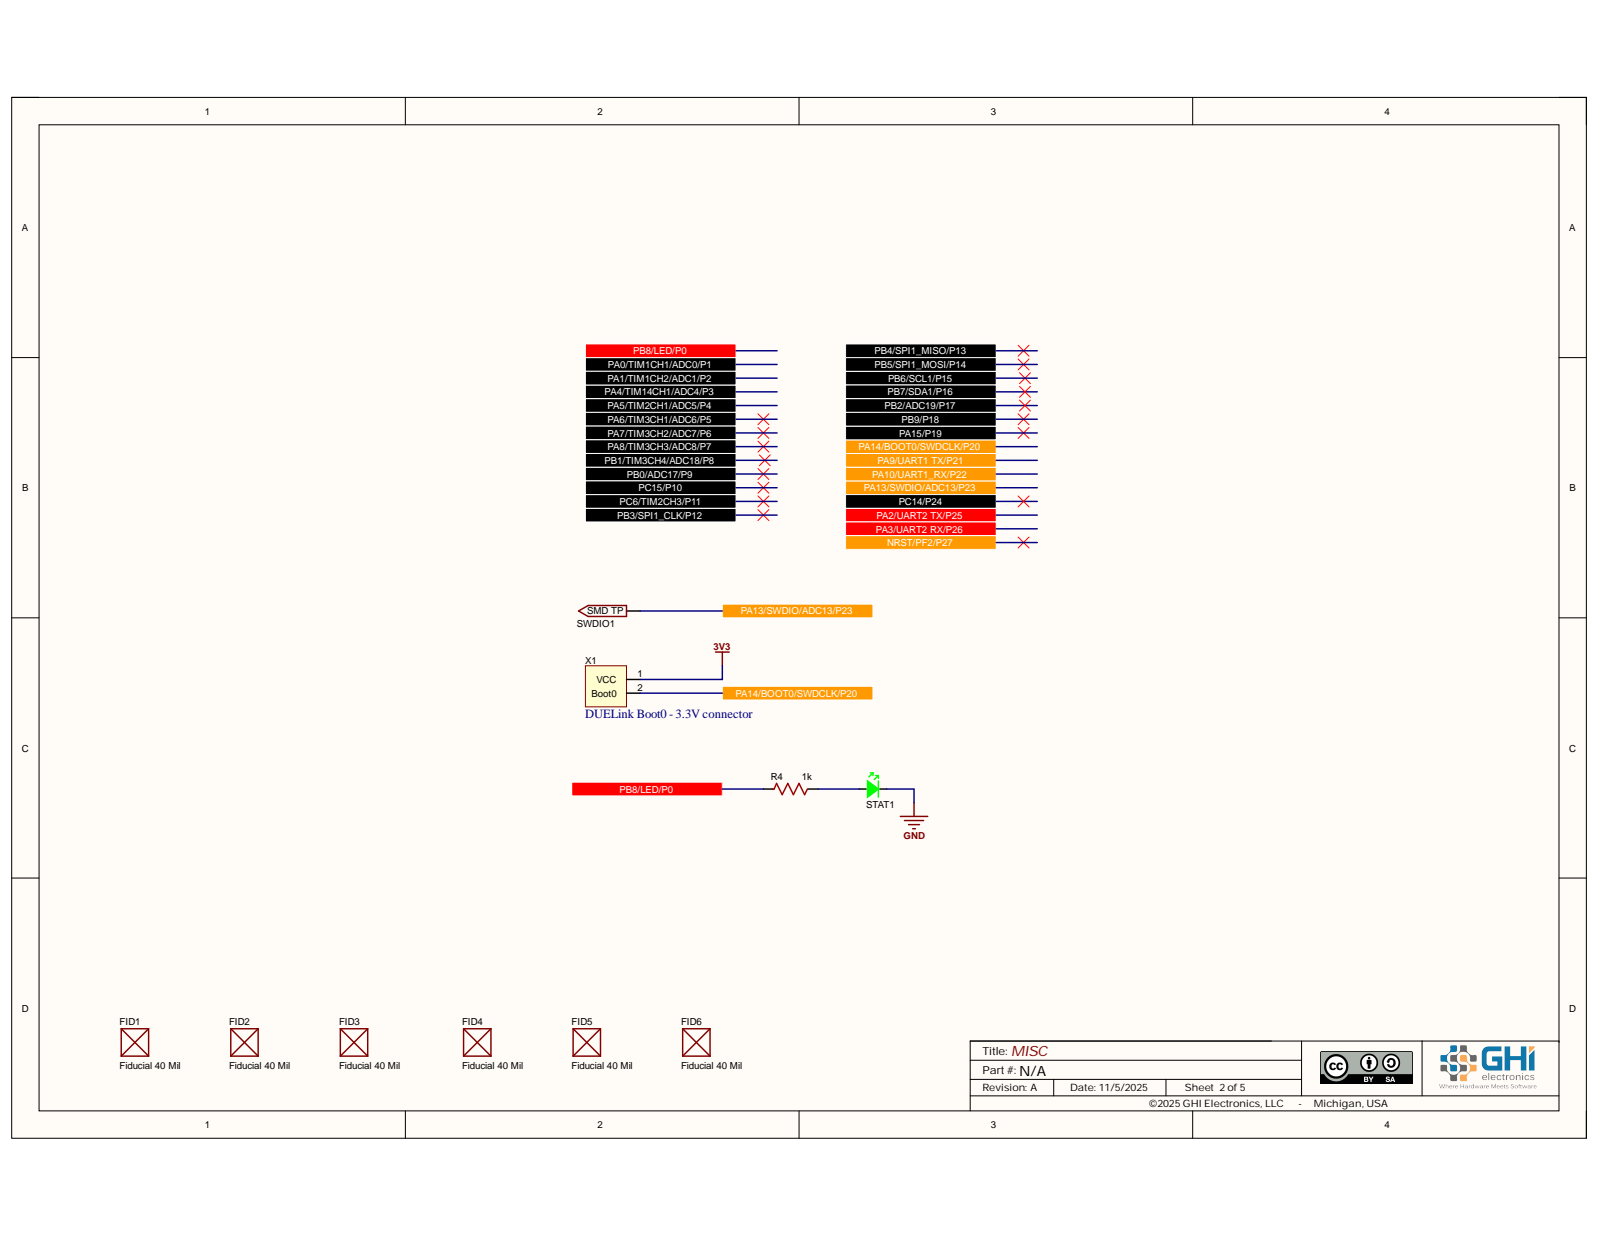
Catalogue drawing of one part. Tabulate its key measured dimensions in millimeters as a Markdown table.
| quantity | value |
| --- | --- |
| part name | PCB; Board; U2; IC_Texas_Instruments_SN74AHC1G09DCKR_eec (+7 more) |
| STEP written by | Open CASCADE 7.5 (AUTOMOTIVE_DESIGN) |
| units | millimeters |
| bodies | 134 solids, 2620 faces (1739 planar, 449 cylindrical, 432 other) |
| overall size | 32 × 29.42 × 12.06 |
| volume | 2 202 mm³ |
| surface area | 3 639 mm² |
| round holes (diameter × count) | 0.8 × 5, 1.02 × 5, 1.42 × 5, 3 × 4, 1.02 × 2 |
| round bosses / shafts (diameter × count) | 2.11 × 5, 4.8 × 1 |
| partial cylindrical surfaces (radius × count) | 0.12 × 35, 0.15 × 14, 0.5 × 4, 3.5 × 4, 0.1 × 3, 0.16 × 2, 0.17 × 2, 0.18 × 2 |
| main face-to-face distances | 1.6, 4.2, 1, 5.8, 2.3, 3, 4.6, 2, 6.9, 5.3 |
| hole center spacings | 2.54, 19.98, 5.08, 5.22, 7.62, 12.05, 12.86, 13.76 |
